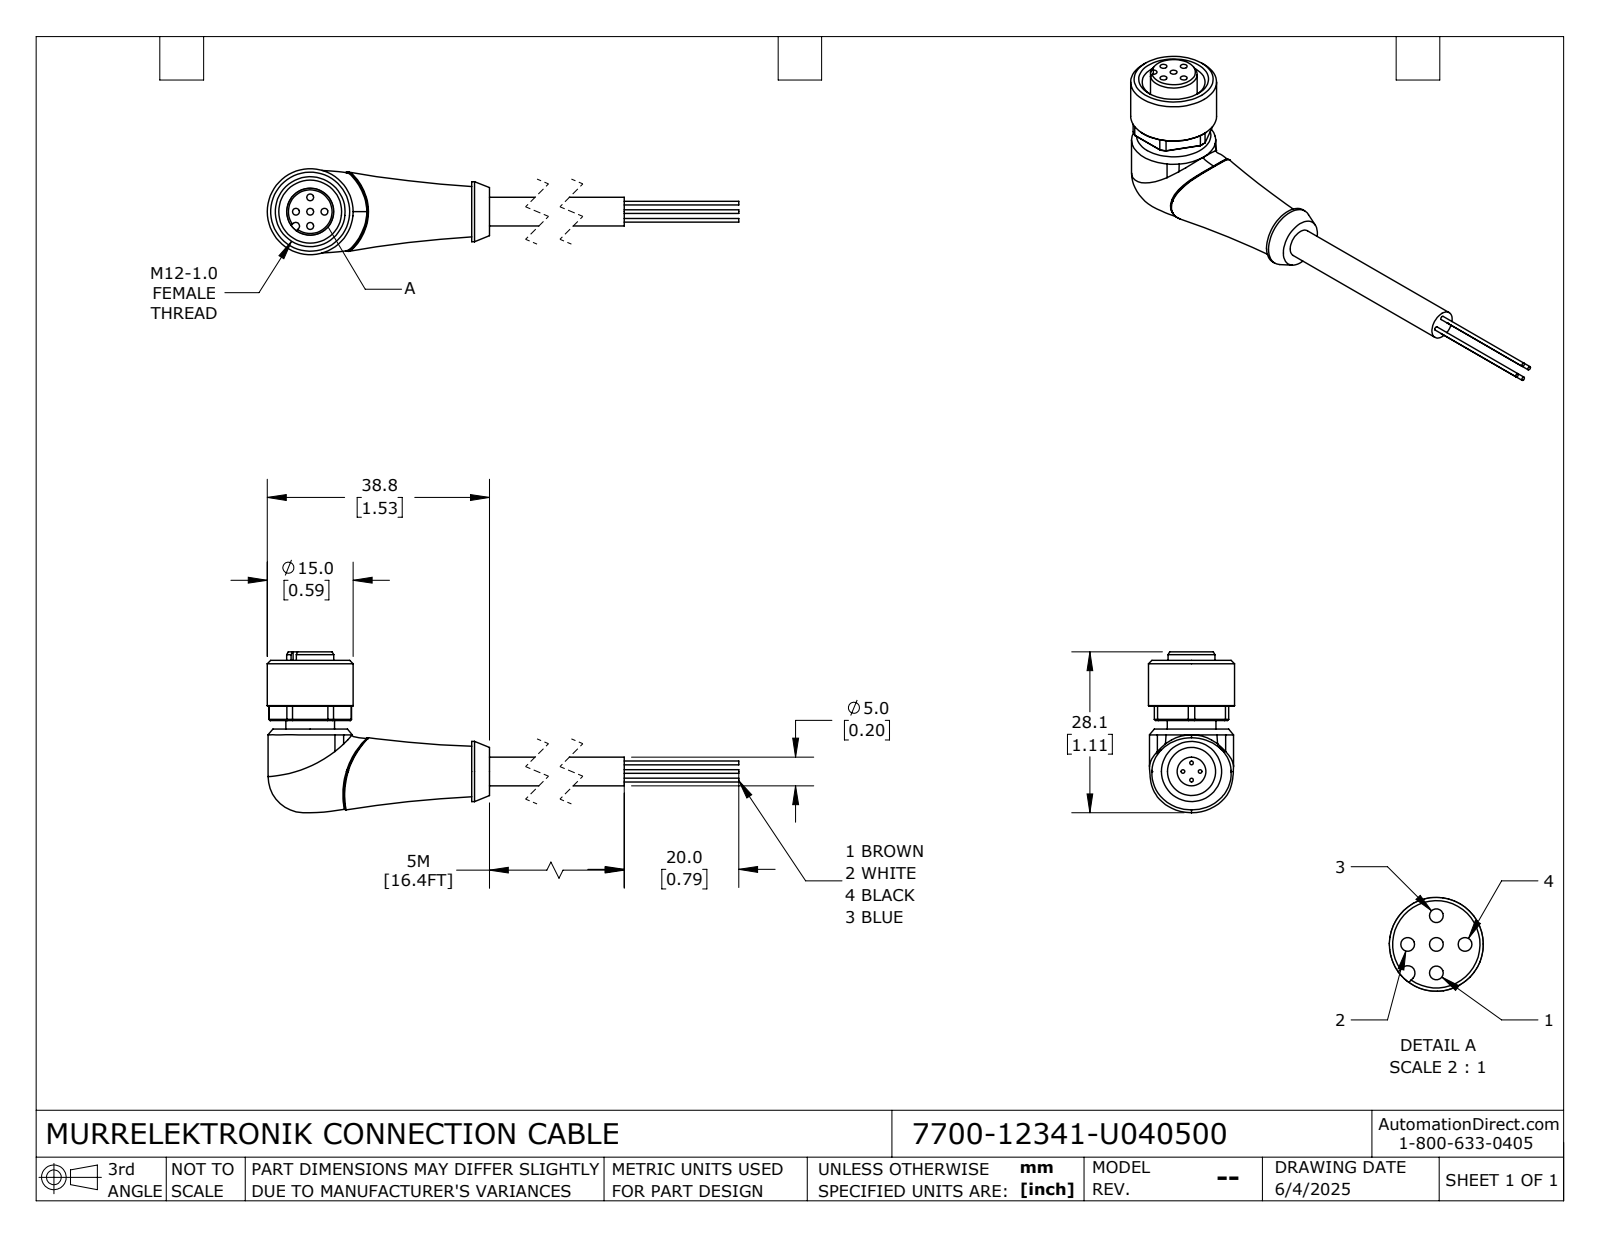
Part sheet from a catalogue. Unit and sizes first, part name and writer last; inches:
Units: inches
Overall size (bounding box): 3.693 × 1.107 × 0.591
Round holes (diameter × count): ⌀0.047 ×5, ⌀0.433 ×1
Round bosses / shafts (diameter × count): ⌀0.025 ×4, ⌀0.591 ×1, ⌀0.413 ×1, ⌀0.335 ×1, ⌀0.323 ×1, ⌀0.197 ×1
Partial cylindrical surfaces — rounded edges, fillets, slot ends (radius × count): R0.026 ×1, R0.283 ×1
Main face-to-face distances: 0.059, 0.472, 0.512, 0.177, 0.118, 0.531, 0.354, 0.413, 0.295, 0.098
Hole centre spacings: 0.098, 0.139, 0.197
Volume: 0.408 in³ · Surface area: 5.805 in²
Bodies: 1 solid, 109 faces (33 planar, 39 cylindrical, 37 other)
Part name (STEP PRODUCT): 7700-12341-U040500
STEP written by: SolidWorks 2024 (CONFIG_CONTROL_DESIGN)
